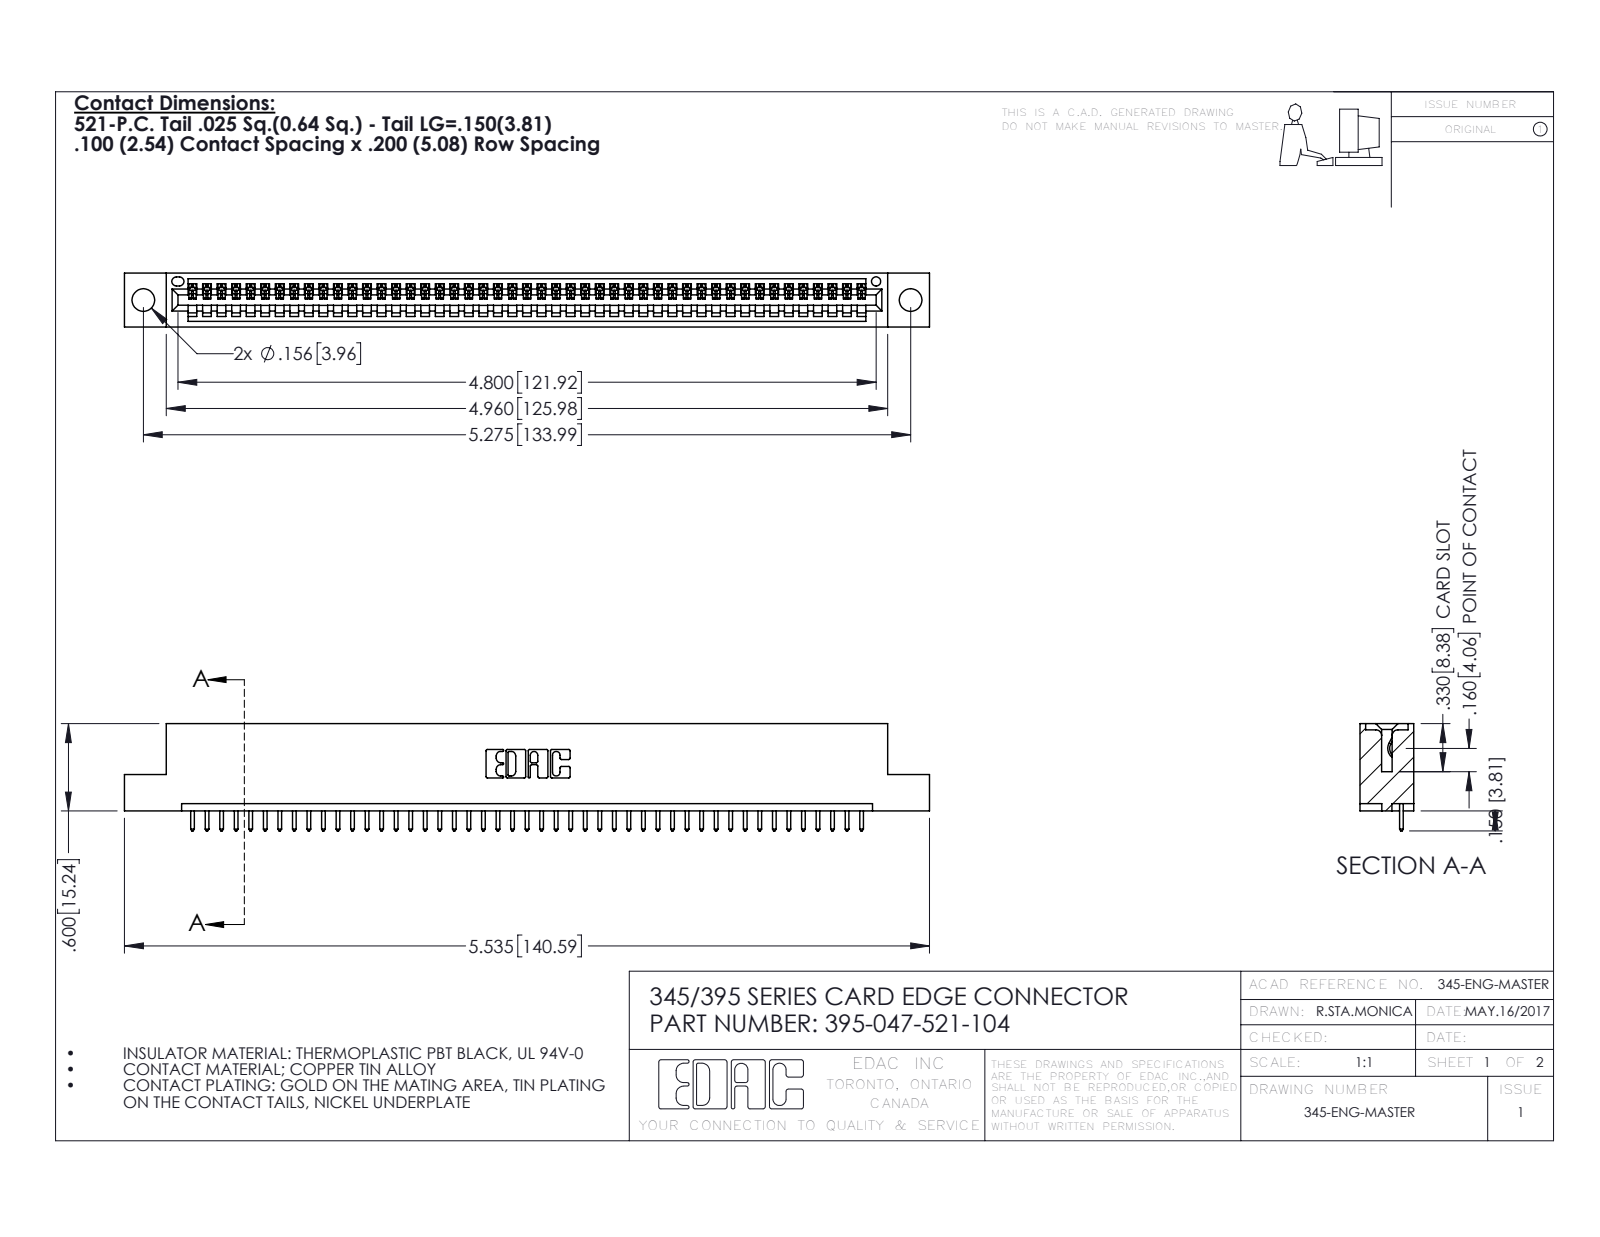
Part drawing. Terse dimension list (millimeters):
name: 345 Part_Flush Mounting Lugs - 0.156 Dia-TH; 345-292-001_345-293-121; 395-047-521-104
written by: SolidWorks 2016 (CONFIG_CONTROL_DESIGN)
unit: mm
bodies: 48 solids, 2852 faces (1960 planar, 892 cylindrical, 0 other)
size: 140.6 × 18.7 × 9.4
volume: 13 200 mm³; area: 16 860 mm²
holes: 2× ⌀4, 1× ⌀1.6
rounds: 94× R0.2, 94× R0.3, 22× R0.3, 6× R0.2, 6× R0.8, 3× R0.7, 2× R0.8, 2× R1
face distances: 7.6, 1.8, 9.4, 5.1, 2.5, 6.9, 0.6, 5.7, 3.8, 1.8
hole spacings: 6.9, 128, 134
